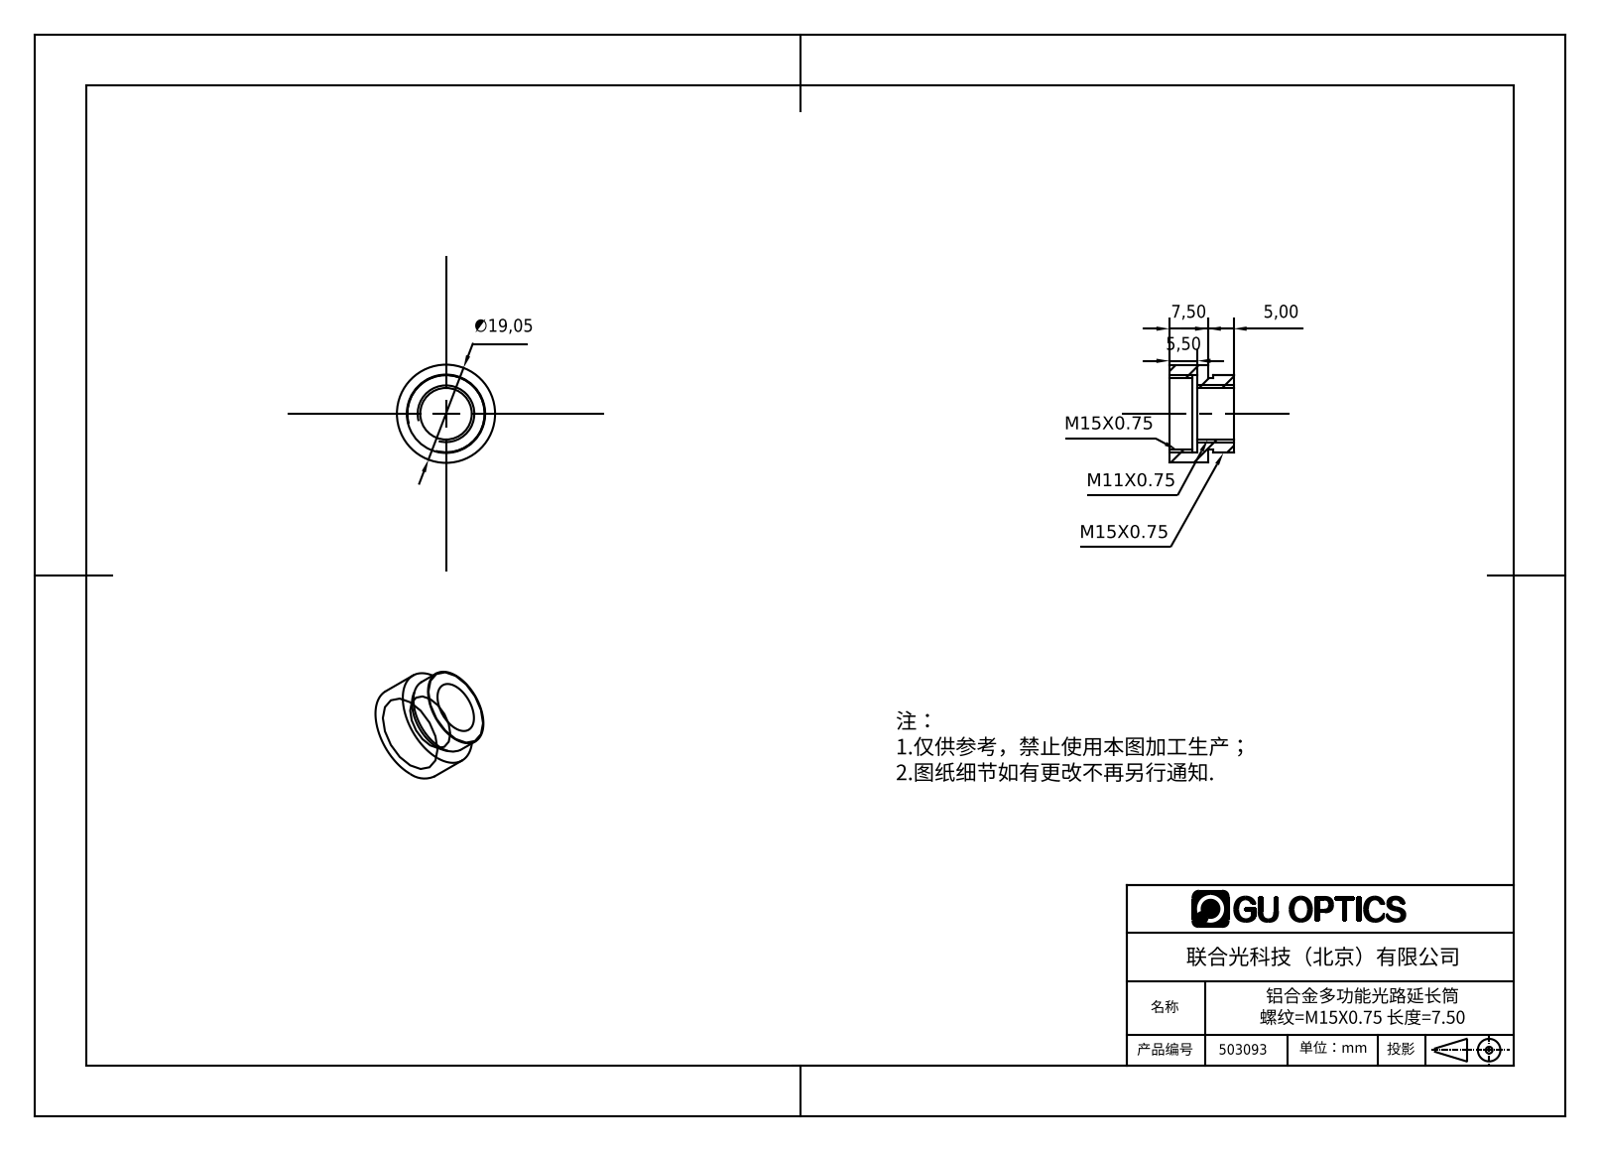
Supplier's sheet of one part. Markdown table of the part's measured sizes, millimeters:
| quantity | value |
| --- | --- |
| part name | 503093 |
| STEP written by | SolidWorks 2016 (AUTOMOTIVE_DESIGN) |
| units | millimeters |
| bodies | 1 solid, 18 faces (6 planar, 12 cylindrical, 0 other) |
| overall size | 19.05 × 19.05 × 12.5 |
| volume | 1 593 mm³ |
| surface area | 1 672 mm² |
| round holes (diameter × count) | 10 × 1, 14 × 1, 15.2 × 1 |
| round bosses / shafts (diameter × count) | 19.05 × 1 |
| main face-to-face distances | 7.5, 5.5, 2, 12.5, 7, 5, 1, 3, 4, 8.5 |
